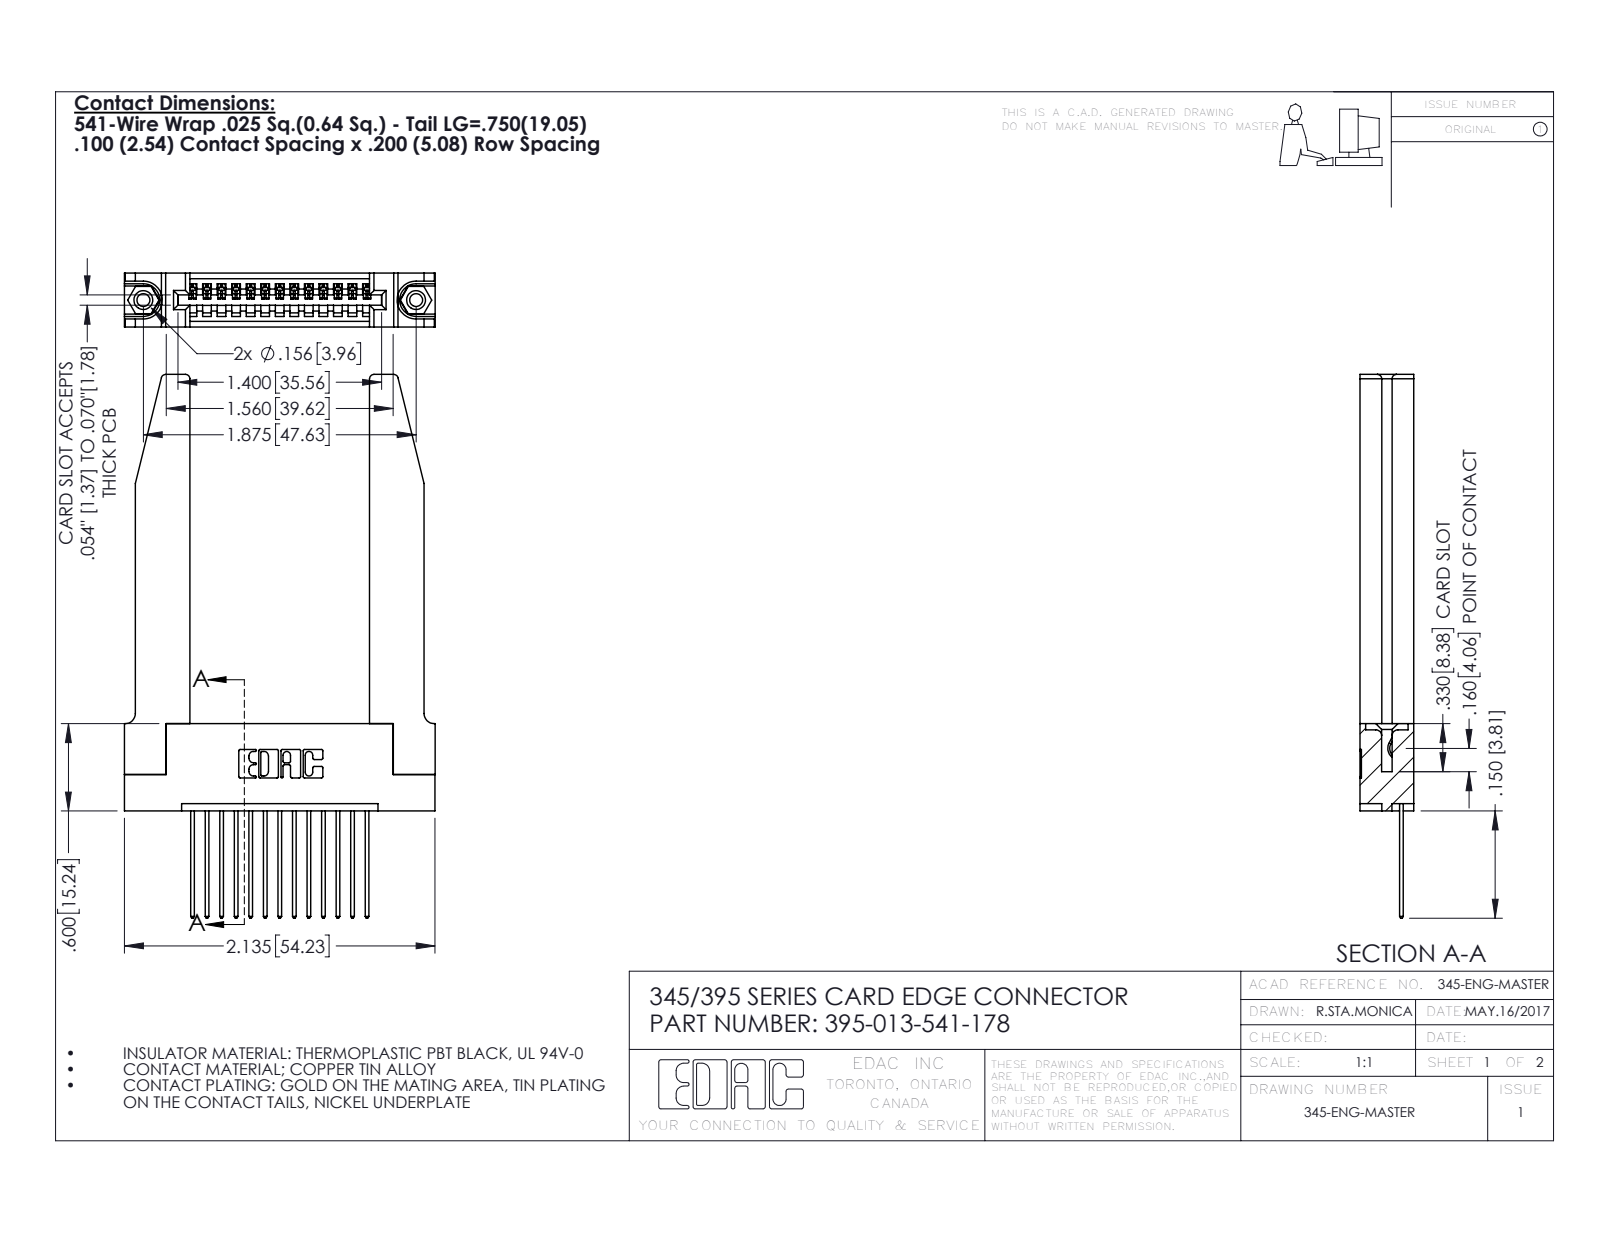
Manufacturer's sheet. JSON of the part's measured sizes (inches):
{"part_name": "395-013-541-178; 345-220-078_345-220-078; 345-292-001_345-293-141; 345 Part_Flush Mounting Lugs - 0.156 Dia-TH (+1 more)", "step_written_by": "SolidWorks 2016 (CONFIG_CONTROL_DESIGN)", "units": "inches", "bodies": {"solids": 18, "faces": 1114, "planar": 742, "cylindrical": 320, "other": 52}, "overall_size": [3.737, 2.136, 0.37], "volume_in3": 0.777, "surface_area_in2": 20.6, "round_holes": [[0.089, 2], [0.125, 2], [0.156, 2], [0.064, 1]], "round_bosses_or_shafts": [[0.155, 2]], "partial_cylinders_radius": [[0.006, 26], [0.01, 26], [0.01, 22], [0.03, 8], [0.007, 6], [0.031, 6], [0.026, 3], [0.031, 2]], "face_to_face_distances": [0.37, 0.072, 0.298, 0.2, 0.148, 0.15, 0.098, 0.272, 0.025, 0.077], "hole_center_spacings": [0.27, 1.643, 1.875]}
